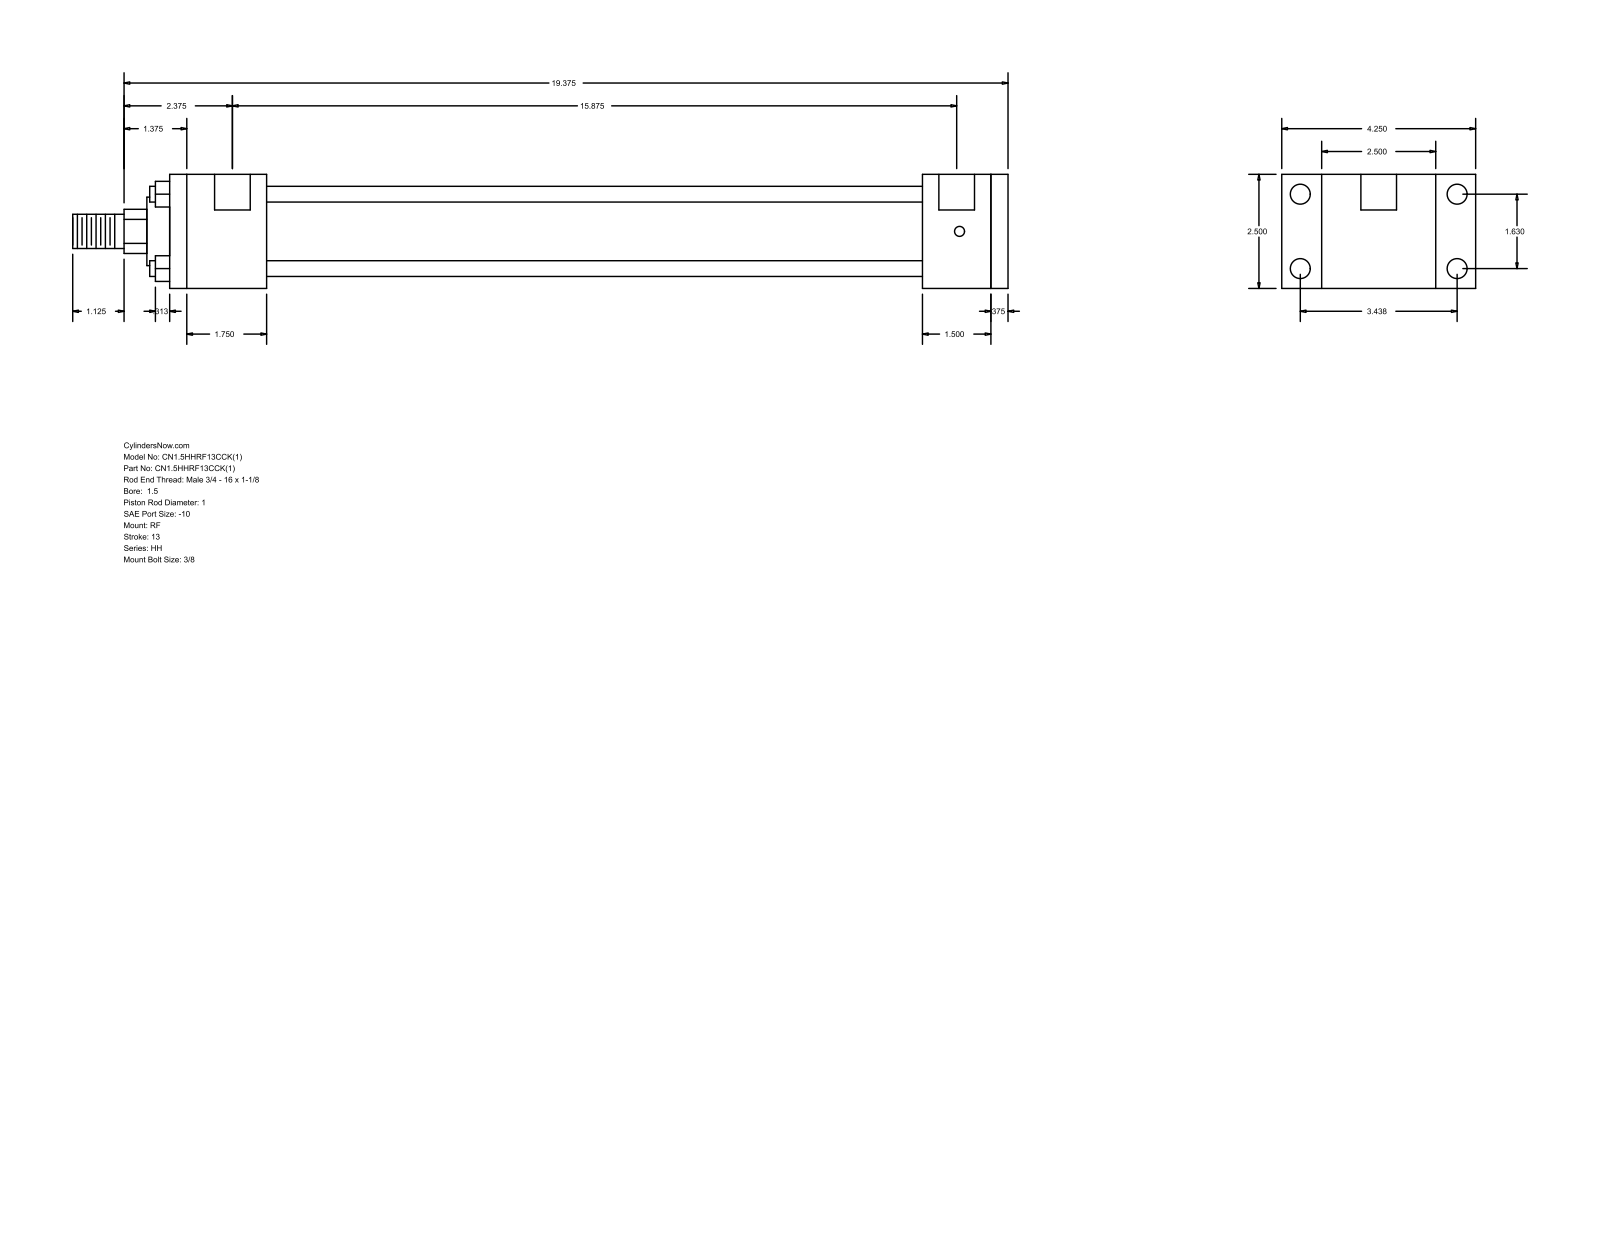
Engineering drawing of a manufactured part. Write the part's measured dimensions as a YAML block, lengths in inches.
part_name: "HH_RF__0150_1"
step_written_by: "GSSL Pune (CONFIG_CONTROL_DESIGN)"
units: inches
bodies: {solids: 0, faces: 92, planar: 64, cylindrical: 28, other: 0}
overall_size: [20.5, 4.25, 2.5]
round_holes:
  - {diameter: 0.219, count: 4}
  - {diameter: 0.438, count: 4}
  - {diameter: 0.781, count: 2}
round_bosses_or_shafts:
  - {diameter: 0.345, count: 4}
  - {diameter: 1.75, count: 1}
  - {diameter: 1.5, count: 1}
  - {diameter: 1, count: 1}
  - {diameter: 0.75, count: 1}
partial_cylinders:
  - {radius: 0.484, count: 1}
face_to_face_distances: [2.5, 0.375, 1.5, 14.375, 15.875, 16.25, 1.875, 2.125, 16.5, 18]
hole_center_spacings: [0.063, 1.63, 3.438, 3.805, 15.937, 16, 15.875]
